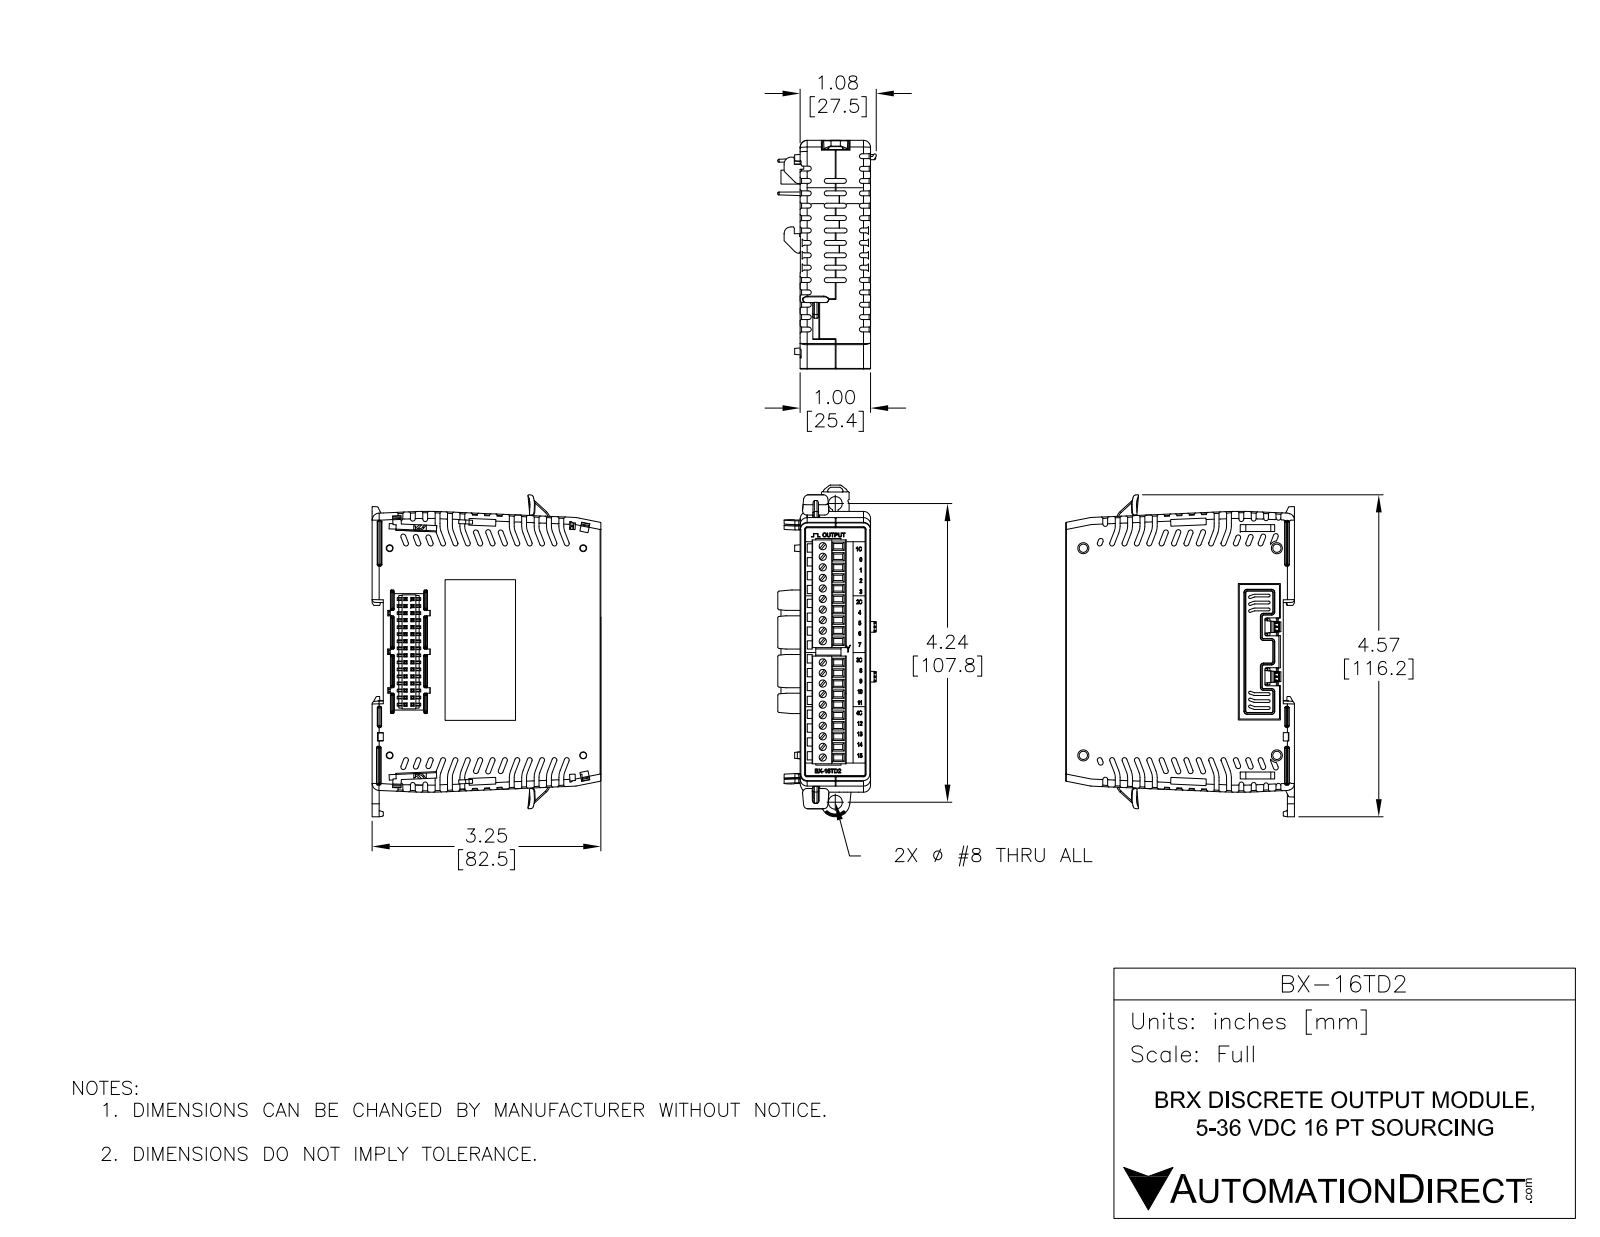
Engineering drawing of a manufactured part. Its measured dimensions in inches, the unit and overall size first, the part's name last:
Units: inches
Overall size (bounding box): 4.586 × 3.25 × 1.402
Round holes (diameter × count): ⌀0.047 ×2, ⌀0.065 ×2, ⌀0.118 ×2, ⌀0.118 ×2, ⌀0.199 ×1
Round bosses / shafts (diameter × count): ⌀0.062 ×2, ⌀0.059 ×2
Partial cylindrical surfaces — rounded edges, fillets, slot ends (radius × count): R0.005 ×102, R0.008 ×101, R0.01 ×47, R0.02 ×34, R0.005 ×24, R0.062 ×20, R0.117 ×14, R0.039 ×13
Main face-to-face distances: 1, 3.211, 3.22, 0.475, 0.039, 0.157, 3.053, 3.063, 0.1, 0.787
Hole centre spacings: 0.1, 0.824, 0.919, 1.3, 2.093, 2.193, 2.585, 2.617
Volume: 11.58 in³ · Surface area: 72.51 in²
Bodies: 12 solids, 4173 faces (2928 planar, 663 cylindrical, 582 other)
Part name (STEP PRODUCT): BX-16TD2
STEP written by: SolidWorks 2017 (AUTOMOTIVE_DESIGN)
